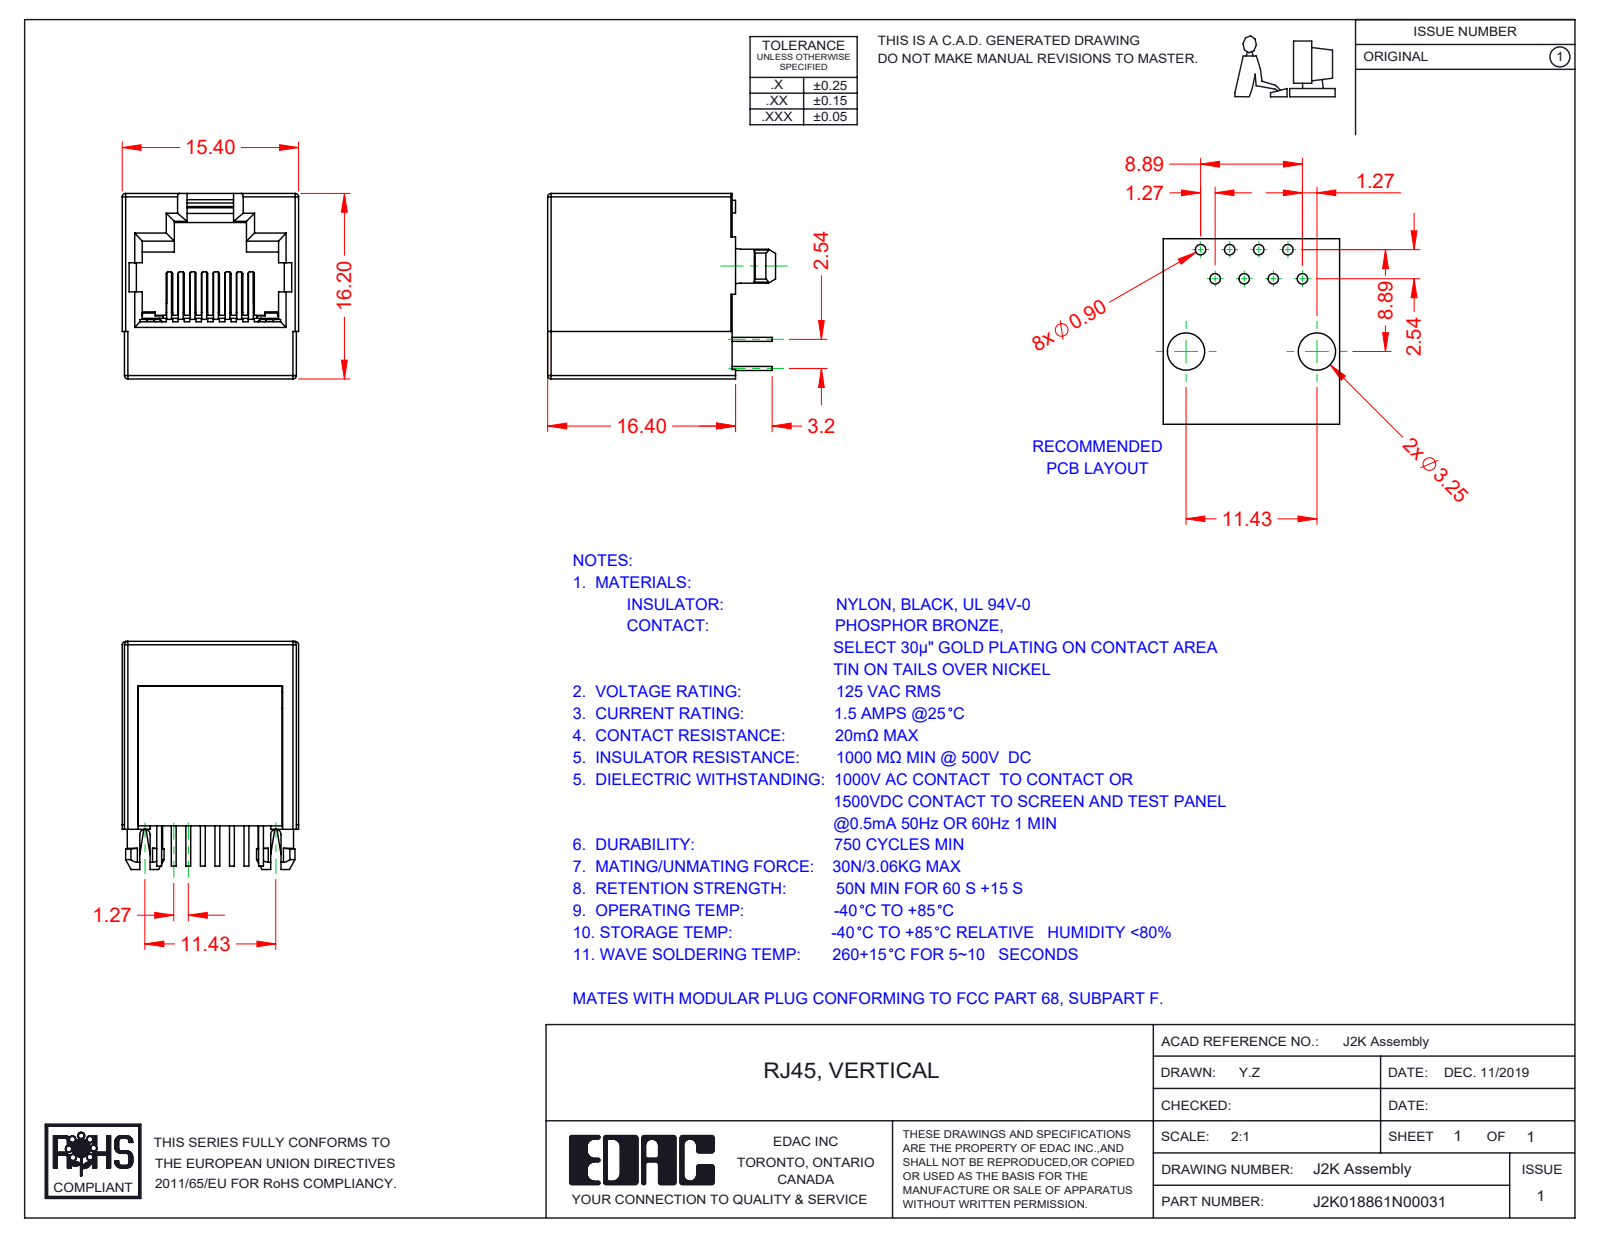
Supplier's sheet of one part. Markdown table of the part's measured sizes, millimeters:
| quantity | value |
| --- | --- |
| part name | RJ2K018861N00031; 2K Contact Lock; 2K Contacts; 2K Insulator |
| STEP written by | SolidWorks 2016 (CONFIG_CONTROL_DESIGN) |
| units | millimeters |
| bodies | 10 solids, 723 faces (586 planar, 113 cylindrical, 24 other) |
| overall size | 19.9 × 16.2 × 15.4 |
| volume | 2 473 mm³ |
| surface area | 3 962 mm² |
| round bosses / shafts (diameter × count) | 3.1 × 2, 1.1 × 2 |
| partial cylindrical surfaces (radius × count) | 0.15 × 16, 0.3 × 10, 0.5 × 3, 0.1 × 2, 0.2 × 2, 0.45 × 2, 0.6 × 2, 0.95 × 2 |
| main face-to-face distances | 16.2, 15.4, 1.4, 14, 1.2, 13.8, 15.2, 0.35, 0.5, 15 |
